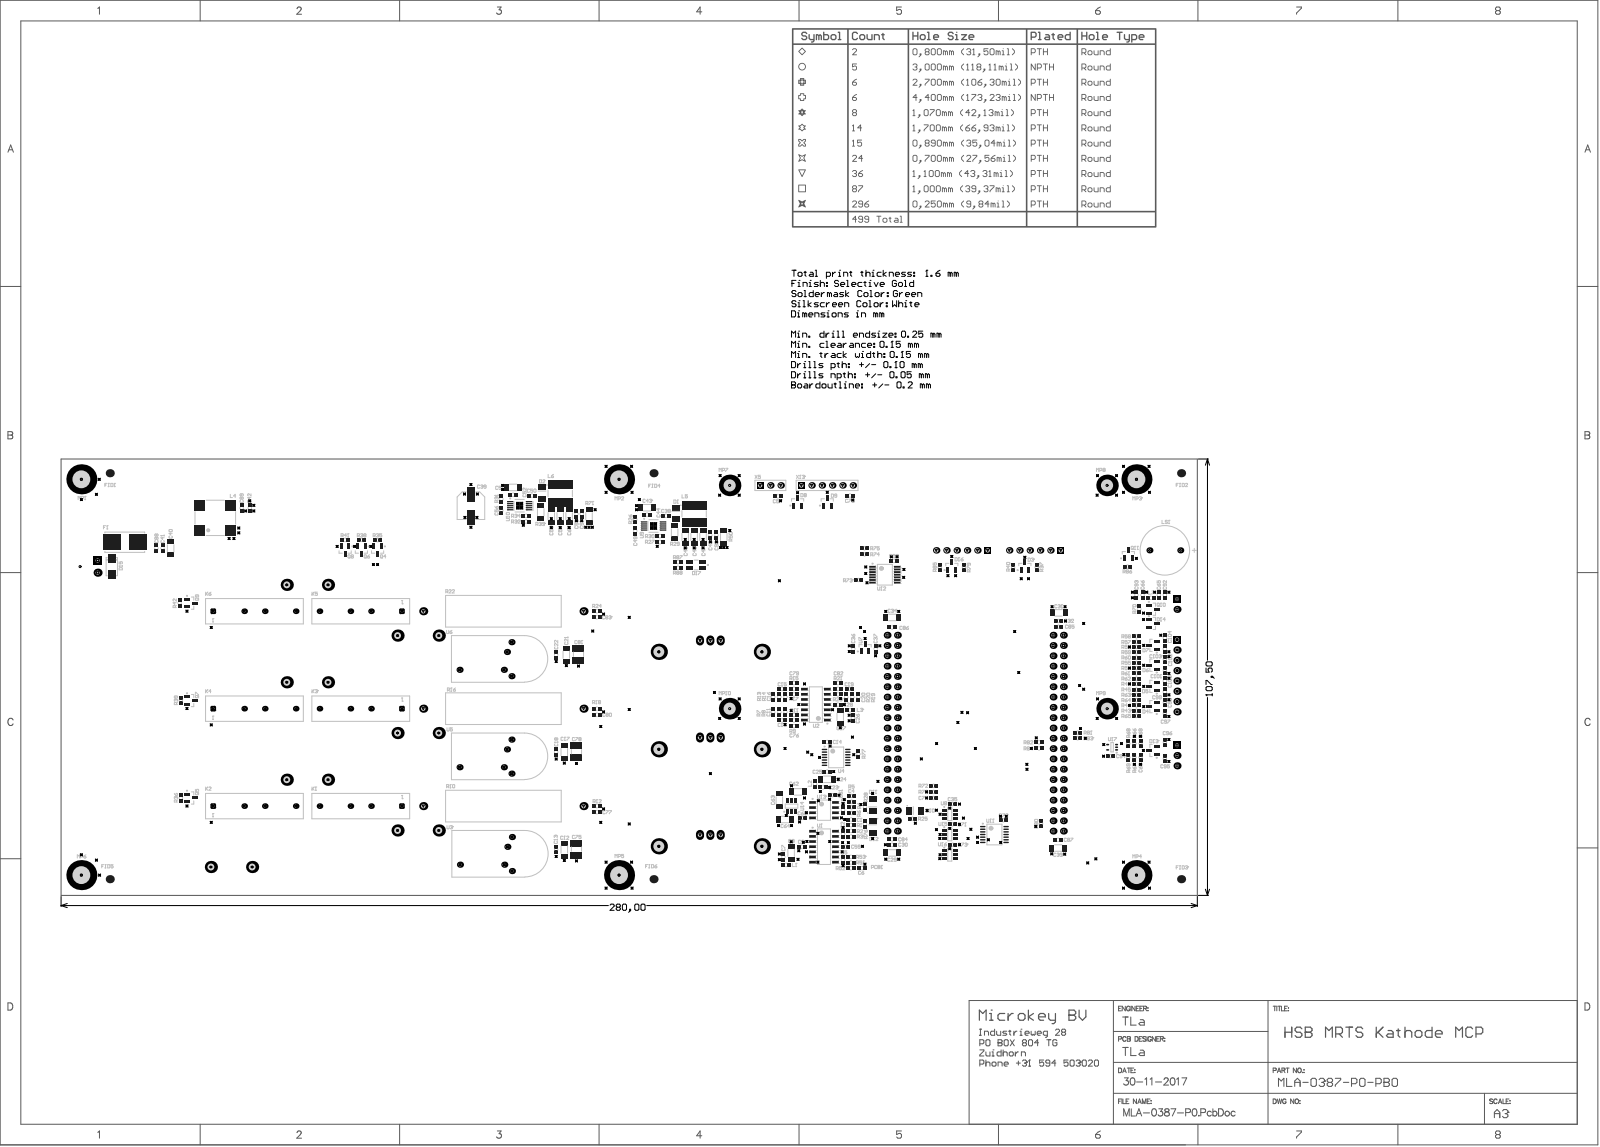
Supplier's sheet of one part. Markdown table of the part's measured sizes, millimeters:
| quantity | value |
| --- | --- |
| part name | PCB; Board; D10; 849027824 (+7 more) |
| STEP written by | Open CASCADE 6.8 (AUTOMOTIVE_DESIGN) |
| units | millimeters |
| bodies | 584 solids, 15010 faces (10464 planar, 2173 cylindrical, 2373 other) |
| overall size | 280 × 107.5 × 53.19 |
| volume | 110 579 mm³ |
| surface area | 124 366 mm² |
| round holes (diameter × count) | 1 × 87, 1.1 × 36, 0.7 × 25, 0.89 × 15, 1.7 × 14, 1.07 × 8, 2.3 × 6, 2.46 × 6, 2.7 × 6, 4.4 × 6, 3 × 5, 1.57 × 4 |
| round bosses / shafts (diameter × count) | 1.8 × 14, 6 × 6, 4.2 × 6, 0.85 × 6, 5.1 × 4, 4.35 × 4, 3.5 × 4, 2.8 × 4 |
| partial cylindrical surfaces (radius × count) | 0.1 × 388, 0.13 × 117, 0.2 × 74, 0.3 × 18, 0.3 × 12, 0.75 × 12, 0.5 × 11, 0.15 × 8 |
| main face-to-face distances | 1.85, 10.39, 12.24, 11.99, 1.6, 13.84, 1.5, 24, 22.75, 5.75 |
| hole center spacings | 24, 7.62, 12.7, 10.16, 20.32, 26.18, 25.18, 27.15 |
